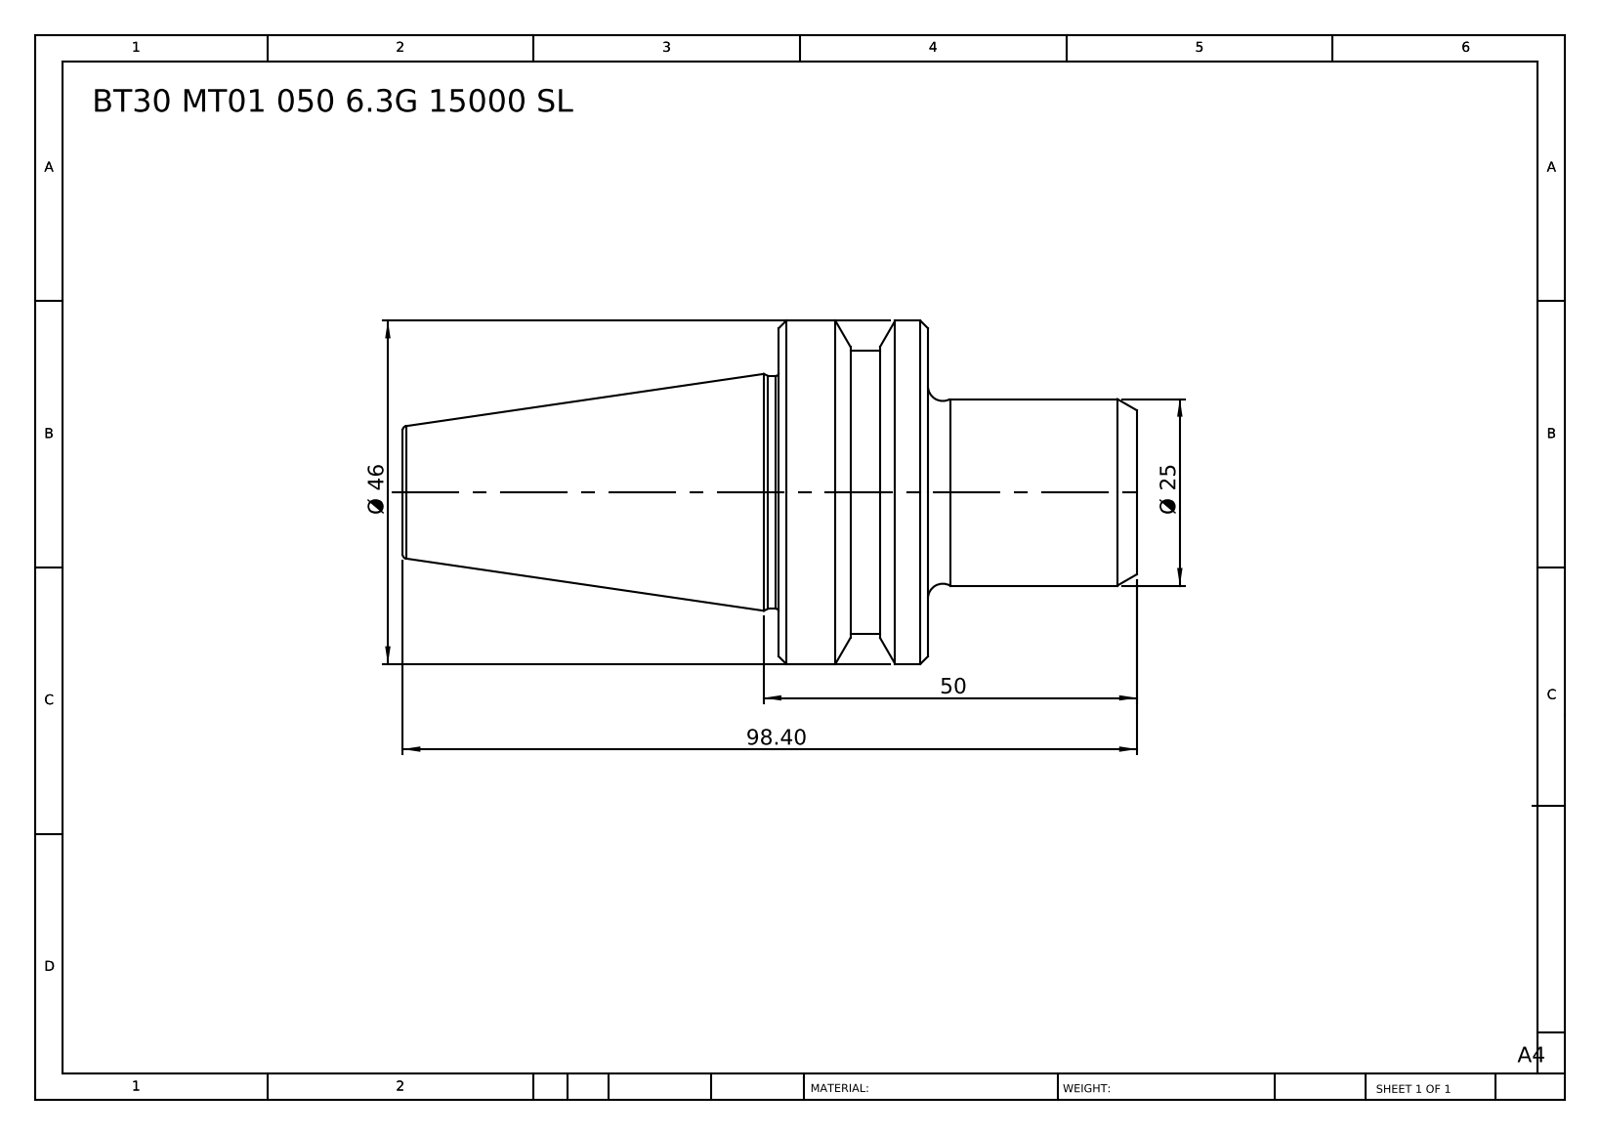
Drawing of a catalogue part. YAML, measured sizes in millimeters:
part_name: "BT30 MT01 050 6.3G 15000 SL"
step_written_by: "SolidWorks 2014 (CONFIG_CONTROL_DESIGN)"
units: millimeters
bodies: {solids: 1, faces: 38, planar: 6, cylindrical: 10, other: 22}
overall_size: [98.4, 46, 46]
volume: 68993
surface_area: 12074
round_bosses_or_shafts:
  - {diameter: 46, count: 1}
  - {diameter: 38, count: 1}
  - {diameter: 31.2, count: 1}
  - {diameter: 25, count: 1}
face_to_face_distances: [20, 28, 48, 98.4, 70.4, 50.4, 38.4, 10.4, 9.6, 60]
